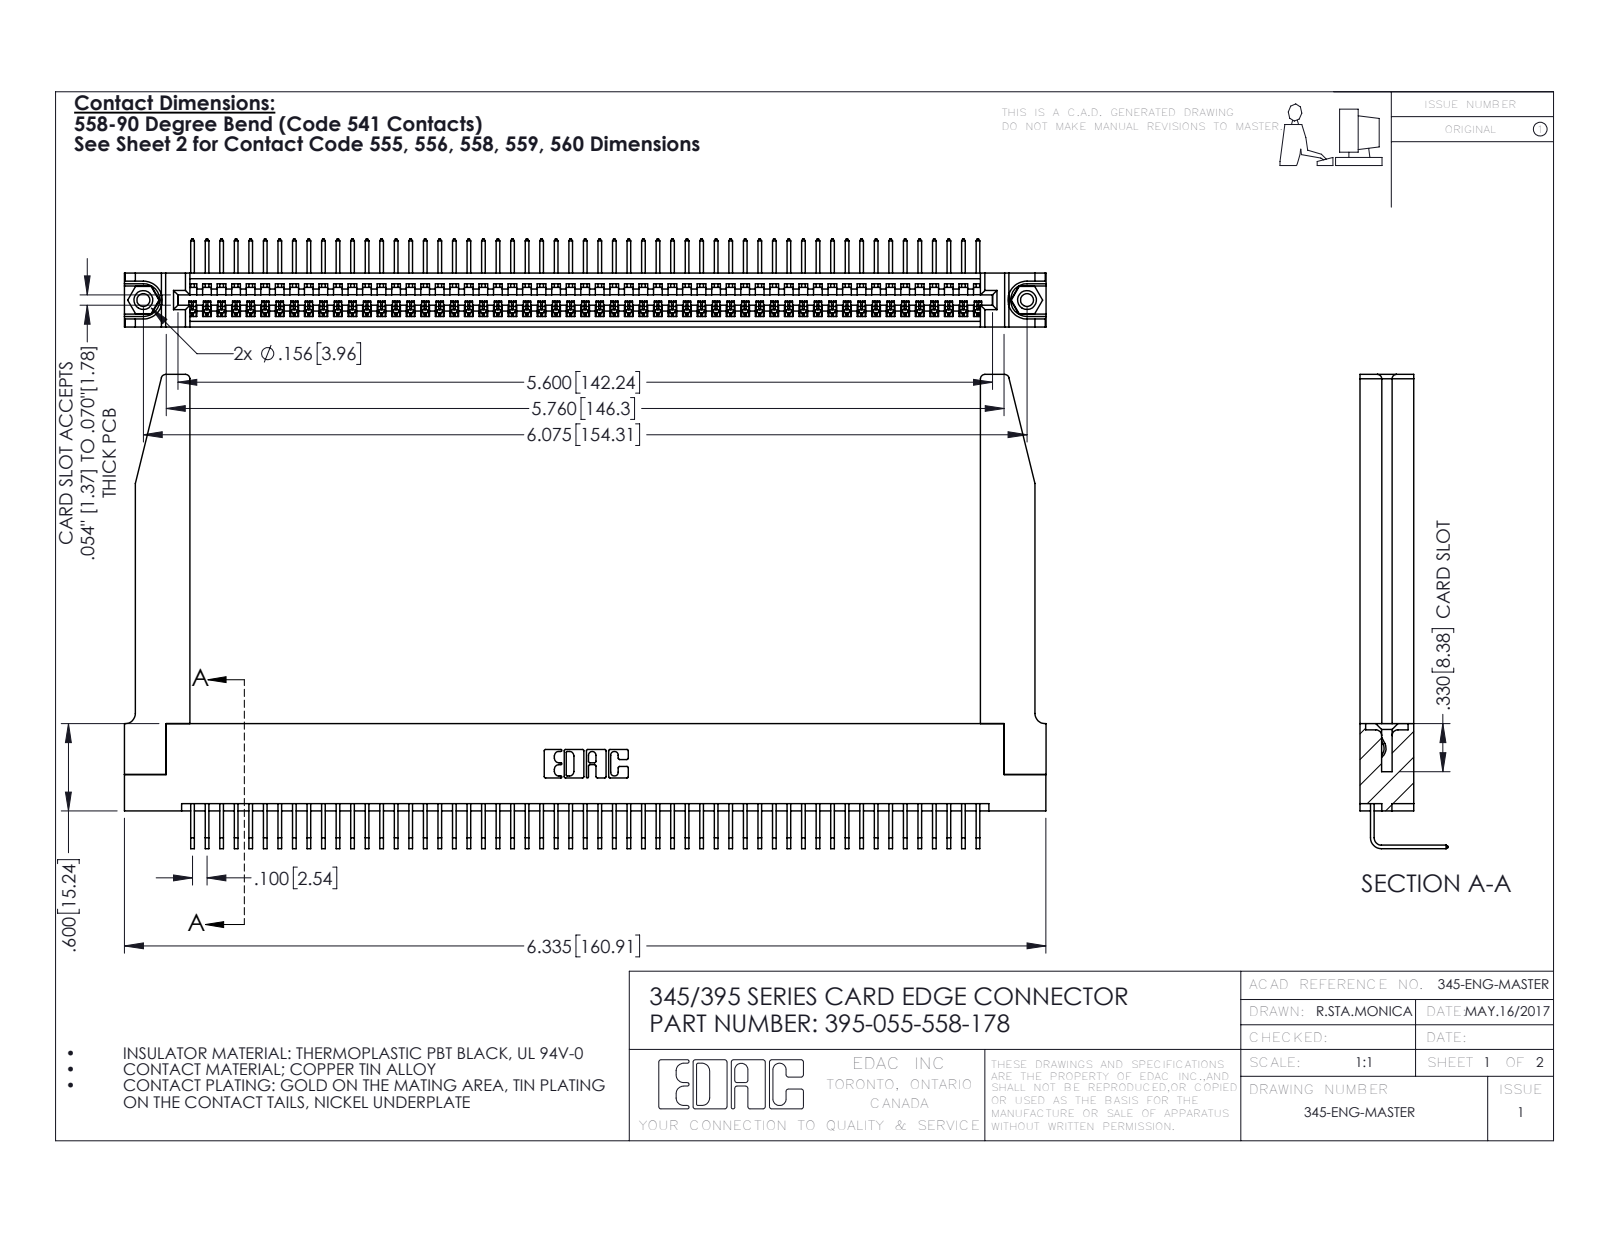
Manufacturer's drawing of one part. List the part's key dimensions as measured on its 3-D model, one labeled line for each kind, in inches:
Part name (STEP PRODUCT): 345-220-078_345-220-078; 395-055-558-178; 345 Part_Flush Mounting Lugs - 0.156 Dia-TH; 345-250-001_345-250-001-102 (+1 more)
STEP written by: SolidWorks 2016 (CONFIG_CONTROL_DESIGN)
Units: inches
Bodies: 60 solids, 3660 faces (2532 planar, 1076 cylindrical, 52 other)
Overall size (bounding box): 6.336 × 3.259 × 0.605
Volume: 1.425 in³ · Surface area: 44.64 in²
Round holes (diameter × count): ⌀0.089 ×2, ⌀0.125 ×2, ⌀0.156 ×2, ⌀0.064 ×1
Round bosses / shafts (diameter × count): ⌀0.155 ×2
Partial cylindrical surfaces — rounded edges, fillets, slot ends (radius × count): R0.006 ×110, R0.01 ×22, R0.03 ×8, R0.007 ×6, R0.031 ×6, R0.026 ×3, R0.031 ×2, R0.04 ×2
Main face-to-face distances: 0.37, 0.072, 0.298, 0.2, 0.098, 0.272, 0.025, 0.225, 0.148, 0.15
Hole centre spacings: 0.27, 5.839, 6.075
